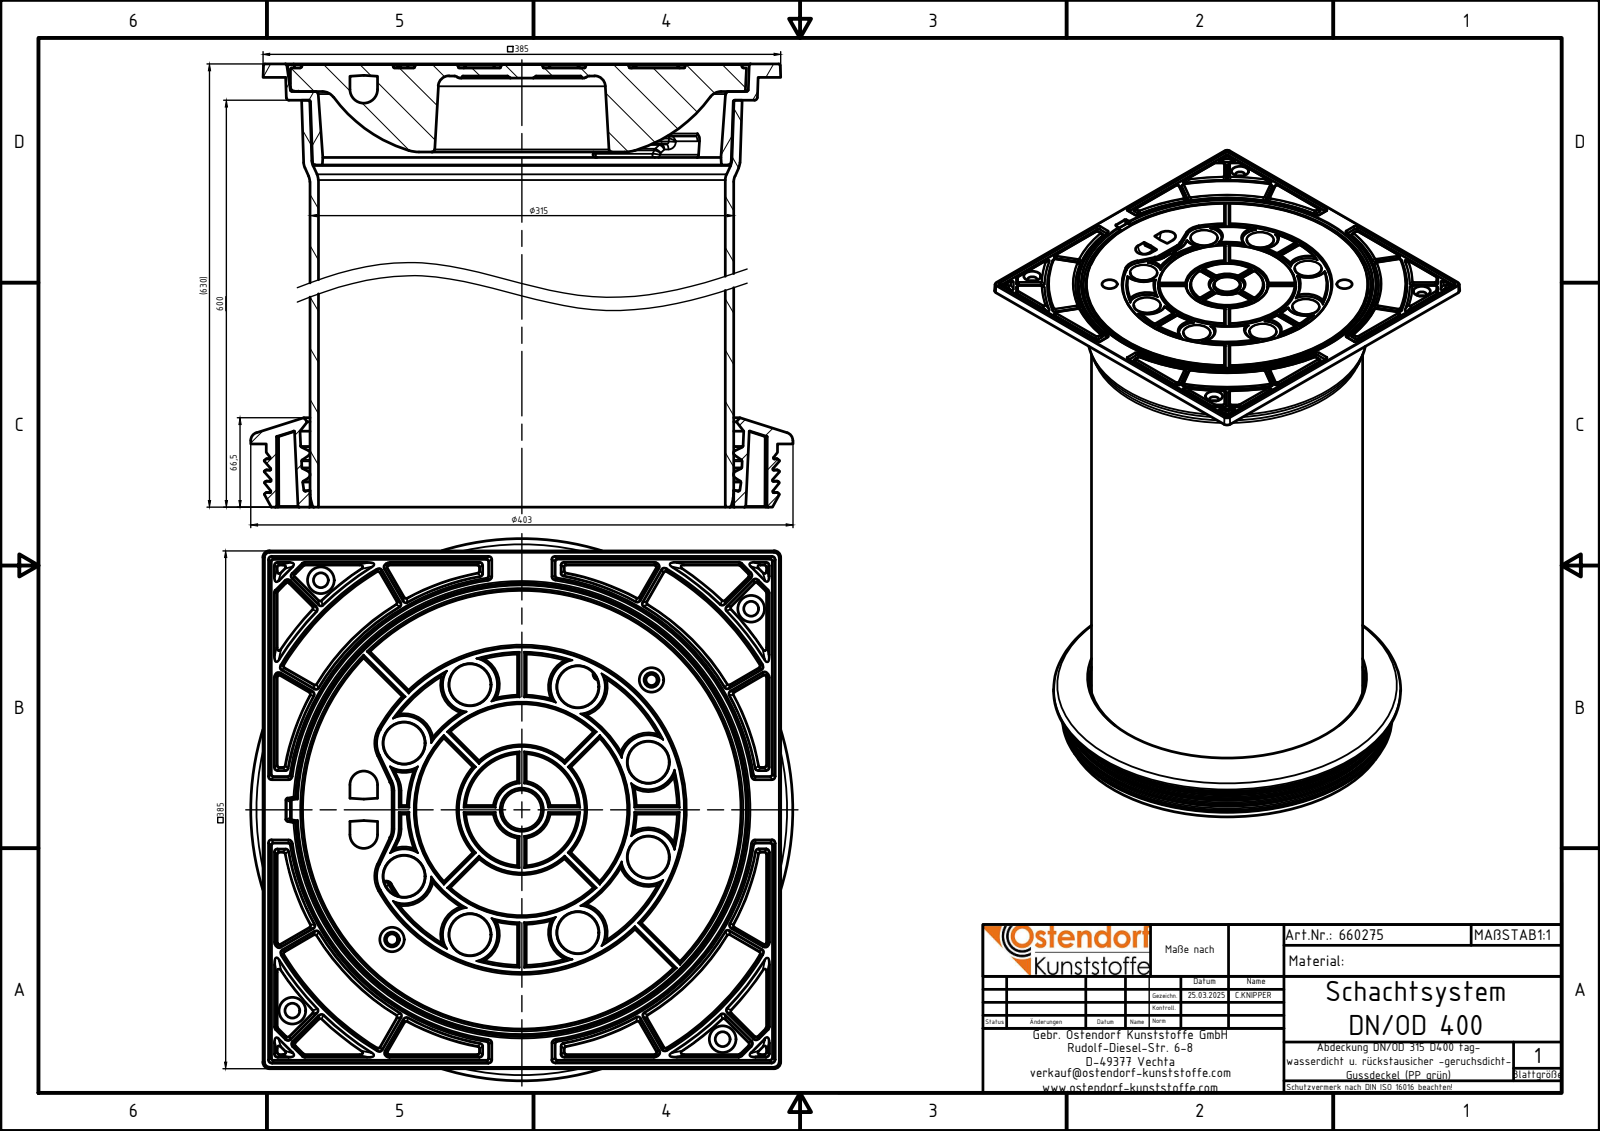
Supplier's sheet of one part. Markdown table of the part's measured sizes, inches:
| quantity | value |
| --- | --- |
| part name | 660275z; 660300z; 990040z; 990040 Teil2z (+1 more) |
| STEP written by | Autodesk Inventor 2024 (AUTOMOTIVE_DESIGN) |
| units | inches |
| bodies | 4 solids, 1847 faces (247 planar, 375 cylindrical, 1225 other) |
| overall size | 24.667 × 15.866 × 15.866 |
| volume | 536.7 in³ |
| surface area | 3 360 in² |
| round holes (diameter × count) | 1.22 × 8, 0.433 × 6, 0.33 × 2, 0.709 × 2, 11.913 × 1, 12.402 × 1 |
| round bosses / shafts (diameter × count) | 15.866 × 1, 14.961 × 1 |
| partial cylindrical surfaces (radius × count) | 0.039 × 211, 0.098 × 48, 0.02 × 16, 0.157 × 8, 0.079 × 4, 0.118 × 1 |
| main face-to-face distances | 0.374, 0.02, 0.394, 0.413, 0.807, 0.787, 0.256, 0.098, 24.647, 0.669 |
| hole center spacings | 3.957, 8.927, 12.625, 2.576, 3.028, 3.156, 5.346, 5.374 |
